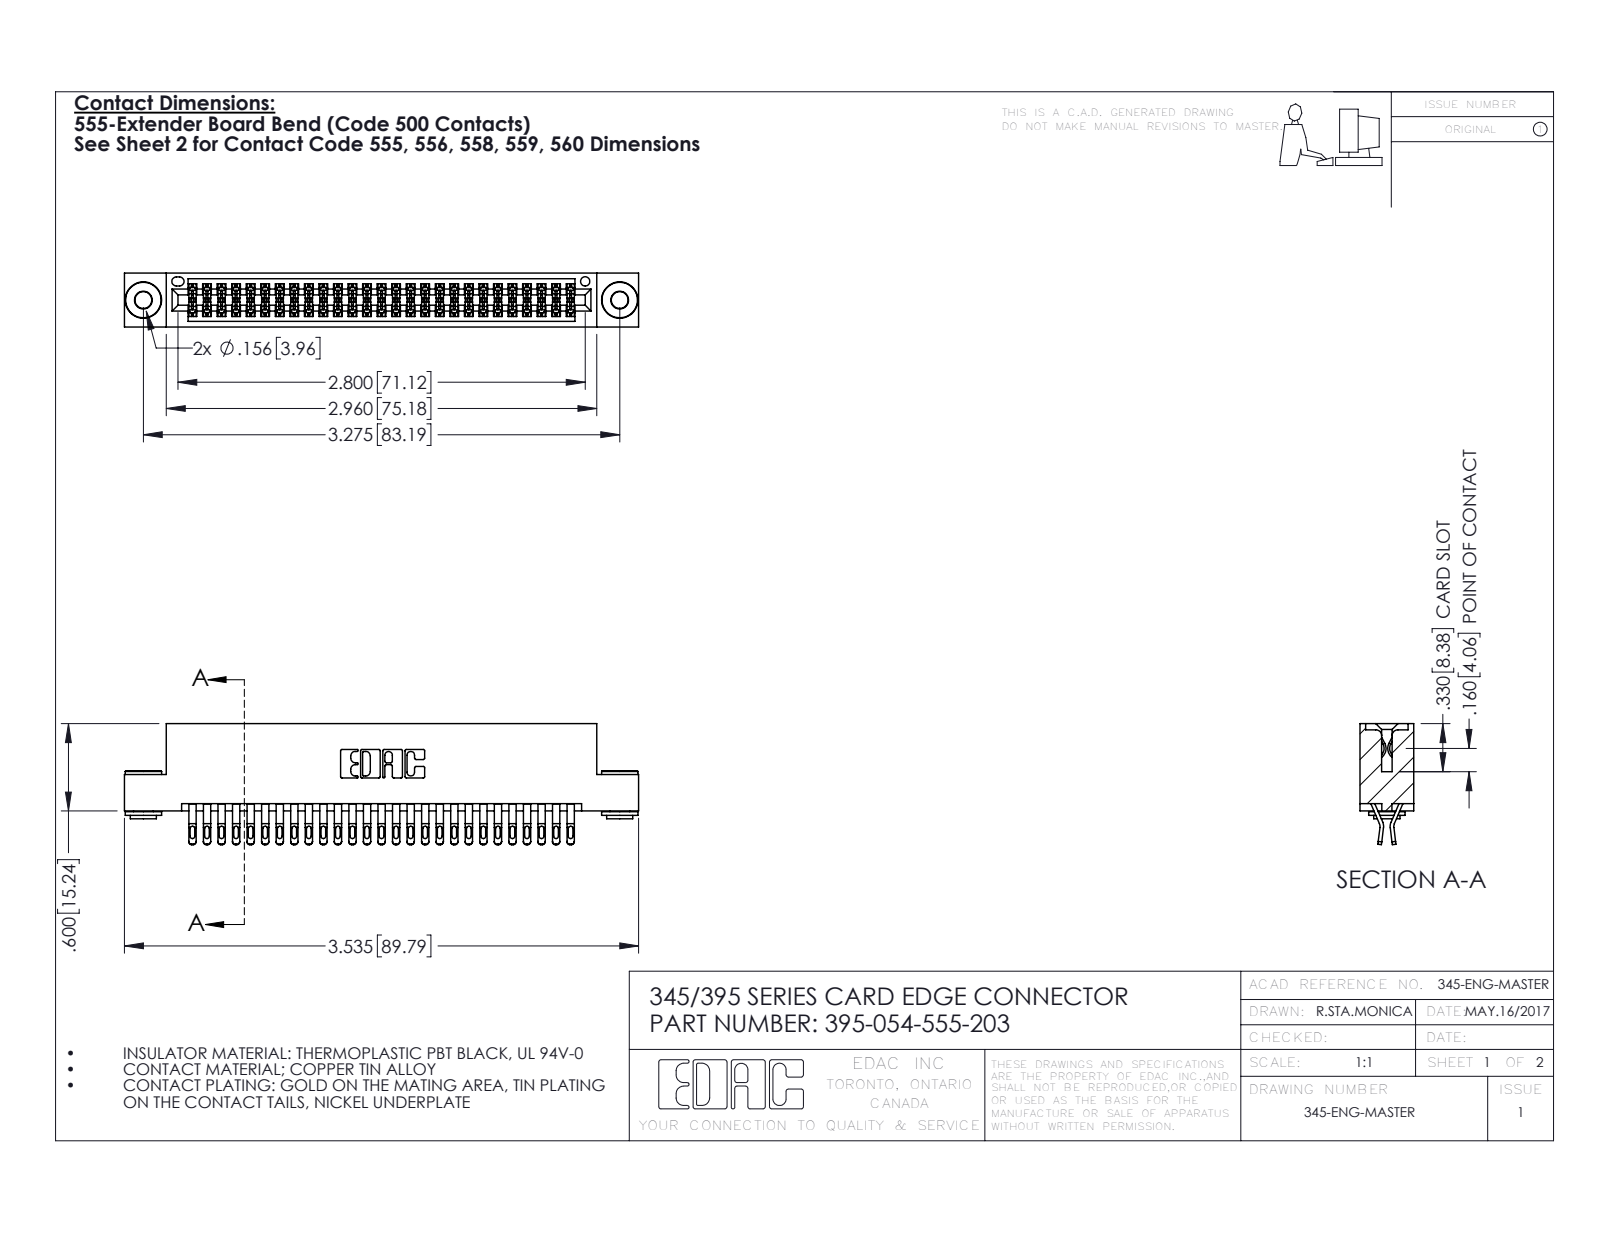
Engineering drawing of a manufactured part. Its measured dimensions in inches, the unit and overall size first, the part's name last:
Units: inches
Overall size (bounding box): 3.535 × 0.832 × 0.37
Round holes (diameter × count): ⌀0.116 ×2, ⌀0.156 ×2, ⌀0.064 ×1
Round bosses / shafts (diameter × count): ⌀0.25 ×2, ⌀0.18 ×2, ⌀0.136 ×2
Partial cylindrical surfaces — rounded edges, fillets, slot ends (radius × count): R0.016 ×135, R0.02 ×108, R0.006 ×81, R0.01 ×22, R0.007 ×6, R0.031 ×6, R0.026 ×3, R0.01 ×2
Main face-to-face distances: 0.072, 0.298, 0.2, 0.025, 0.37, 0.098, 0.272, 0.225, 0.175, 0.149
Hole centre spacings: 0.27, 3.04, 3.275
Volume: 0.535 in³ · Surface area: 20.78 in²
Bodies: 57 solids, 3188 faces (1764 planar, 1416 cylindrical, 8 other)
Part name (STEP PRODUCT): 345-250-002_345-250-002-102; 345-292-001_555 Tail; 395-054-555-203; 345 Part_Flush Mounting Lugs - 0.156 Dia-TH
STEP written by: SolidWorks 2016 (CONFIG_CONTROL_DESIGN)
